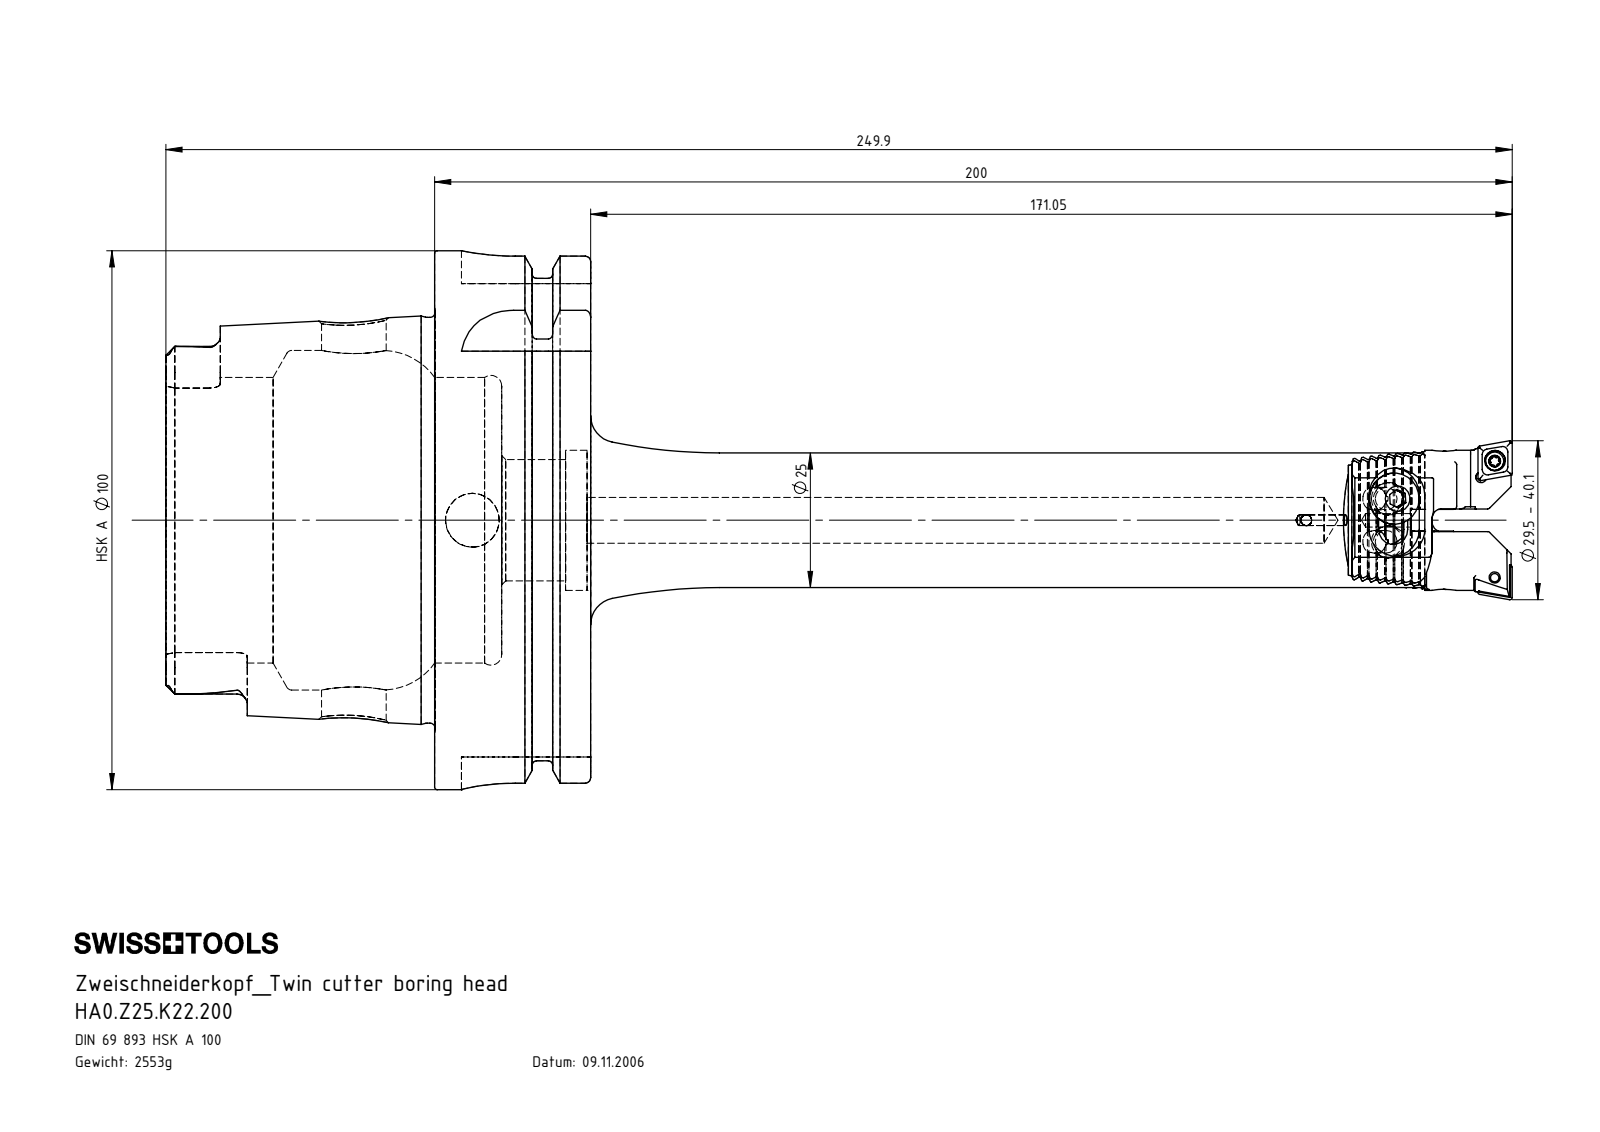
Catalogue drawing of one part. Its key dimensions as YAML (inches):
part_name: "Z25-WCA.001.016; CCMT060204; Z25-ER1.002.012_A; HA0.Z25.K22.200 (+7 more)"
step_written_by: "SolidWorks 2022 (CONFIG_CONTROL_DESIGN)"
units: inches
bodies: {solids: 14, faces: 1073, planar: 496, cylindrical: 280, other: 297}
overall_size: [9.839, 3.937, 3.937]
volume: 19.88
surface_area: 111
round_holes:
  - {diameter: 0.079, count: 5}
  - {diameter: 0.063, count: 2}
  - {diameter: 0.081, count: 2}
  - {diameter: 0.11, count: 2}
  - {diameter: 0.152, count: 2}
  - {diameter: 0.165, count: 2}
  - {diameter: 0.209, count: 2}
  - {diameter: 0.236, count: 2}
  - {diameter: 0.098, count: 1}
  - {diameter: 0.138, count: 1}
  - {diameter: 0.335, count: 1}
  - {diameter: 0.394, count: 1}
round_bosses_or_shafts:
  - {diameter: 0.374, count: 2}
  - {diameter: 0.362, count: 2}
  - {diameter: 0.197, count: 2}
  - {diameter: 0.134, count: 2}
  - {diameter: 0.098, count: 2}
  - {diameter: 3.937, count: 1}
  - {diameter: 3.62, count: 1}
  - {diameter: 2.963, count: 1}
partial_cylinders:
  - {radius: 0.005, count: 18}
  - {radius: 0.02, count: 18}
  - {radius: 0.005, count: 16}
  - {radius: 0.008, count: 12}
  - {radius: 0.014, count: 10}
  - {radius: 0.075, count: 6}
  - {radius: 0.079, count: 4}
  - {radius: 0.11, count: 4}
face_to_face_distances: [1.14, 0.49, 0.65, 0.056, 1.965, 2.455, 3.104, 0.113, 0.026, 3.079]
hole_center_spacings: [0.154, 0.157, 0.276, 0.709, 0.713, 0.823, 8.042, 0.532]
